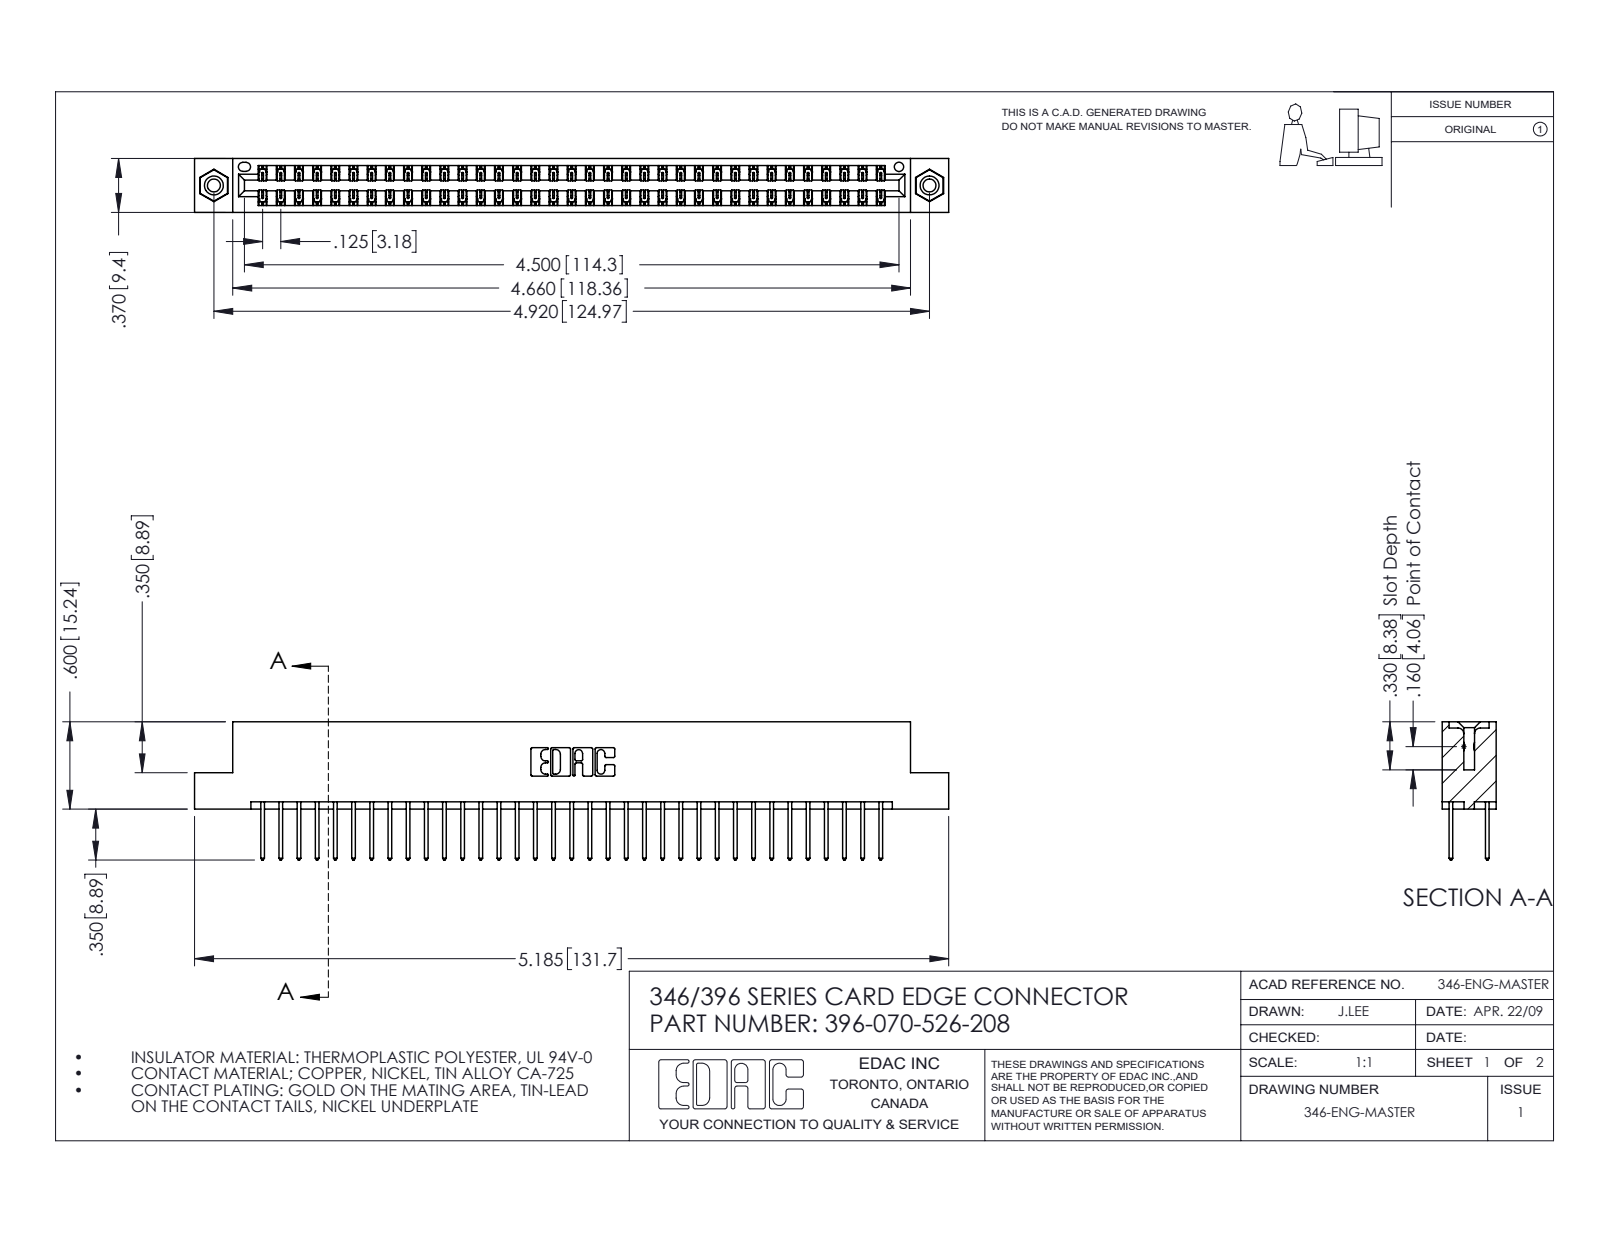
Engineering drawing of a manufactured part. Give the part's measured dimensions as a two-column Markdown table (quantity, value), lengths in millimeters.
| quantity | value |
| --- | --- |
| part name | 346 Part_Flush Mounting Lugs - 0.156 Dia-TI; 396-070-526-208; 345-292-001_345-293-126; 345-250-001_345-250-003-102 |
| STEP written by | SolidWorks 2016 (CONFIG_CONTROL_DESIGN) |
| units | millimeters |
| bodies | 73 solids, 3822 faces (2558 planar, 1248 cylindrical, 16 other) |
| overall size | 131.7 × 24.1 × 9.4 |
| volume | 12 900 mm³ |
| surface area | 18 150 mm² |
| round holes (diameter × count) | 2.3 × 2, 3.2 × 2, 4 × 2, 1.6 × 1 |
| round bosses / shafts (diameter × count) | 3.9 × 2 |
| partial cylindrical surfaces (radius × count) | 0.2 × 105, 0.3 × 70, 0.3 × 22, 0.2 × 6, 0.8 × 6, 0.7 × 3, 0.4 × 2, 0.6 × 2 |
| main face-to-face distances | 1.2, 8.2, 6.4, 9.4, 1.8, 7.6, 0.6, 7, 3.8, 5.6 |
| hole center spacings | 6.2, 119.7, 125 |
